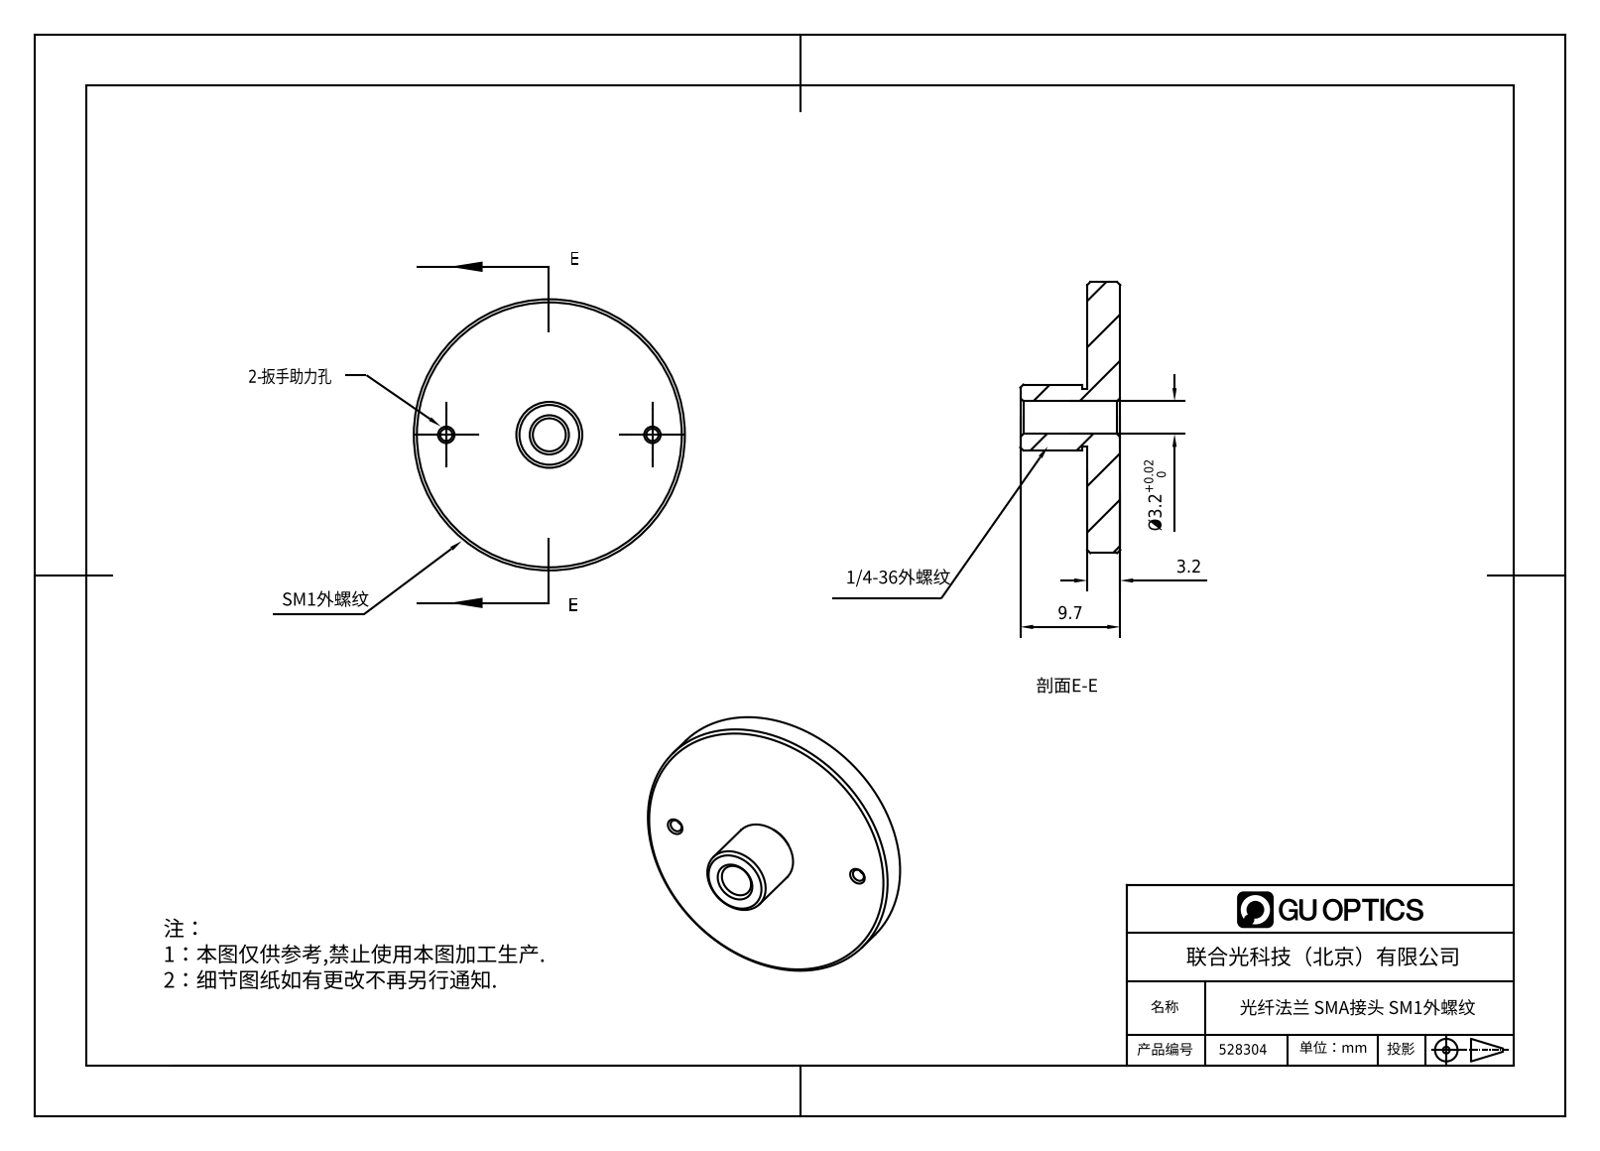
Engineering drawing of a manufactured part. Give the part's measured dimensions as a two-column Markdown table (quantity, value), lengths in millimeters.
| quantity | value |
| --- | --- |
| part name | 528304，光纤法兰 SMA接头 SM1外螺纹 |
| STEP written by | SolidWorks 2020 (CONFIG_CONTROL_DESIGN) |
| units | millimeters |
| bodies | 1 solid, 32 faces (6 planar, 12 cylindrical, 14 other) |
| overall size | 26.3 × 26.3 × 9.7 |
| volume | 1 853 mm³ |
| surface area | 1 551 mm² |
| round holes (diameter × count) | 1.2 × 2, 3.2 × 1 |
| round bosses / shafts (diameter × count) | 26.3 × 1, 6.4 × 1, 5.6 × 1 |
| main face-to-face distances | 3.2, 9.7, 6.5, 3.7, 0.5, 6, 1.7, 1.5, 2, 8 |
| hole center spacings | 10, 20 |
